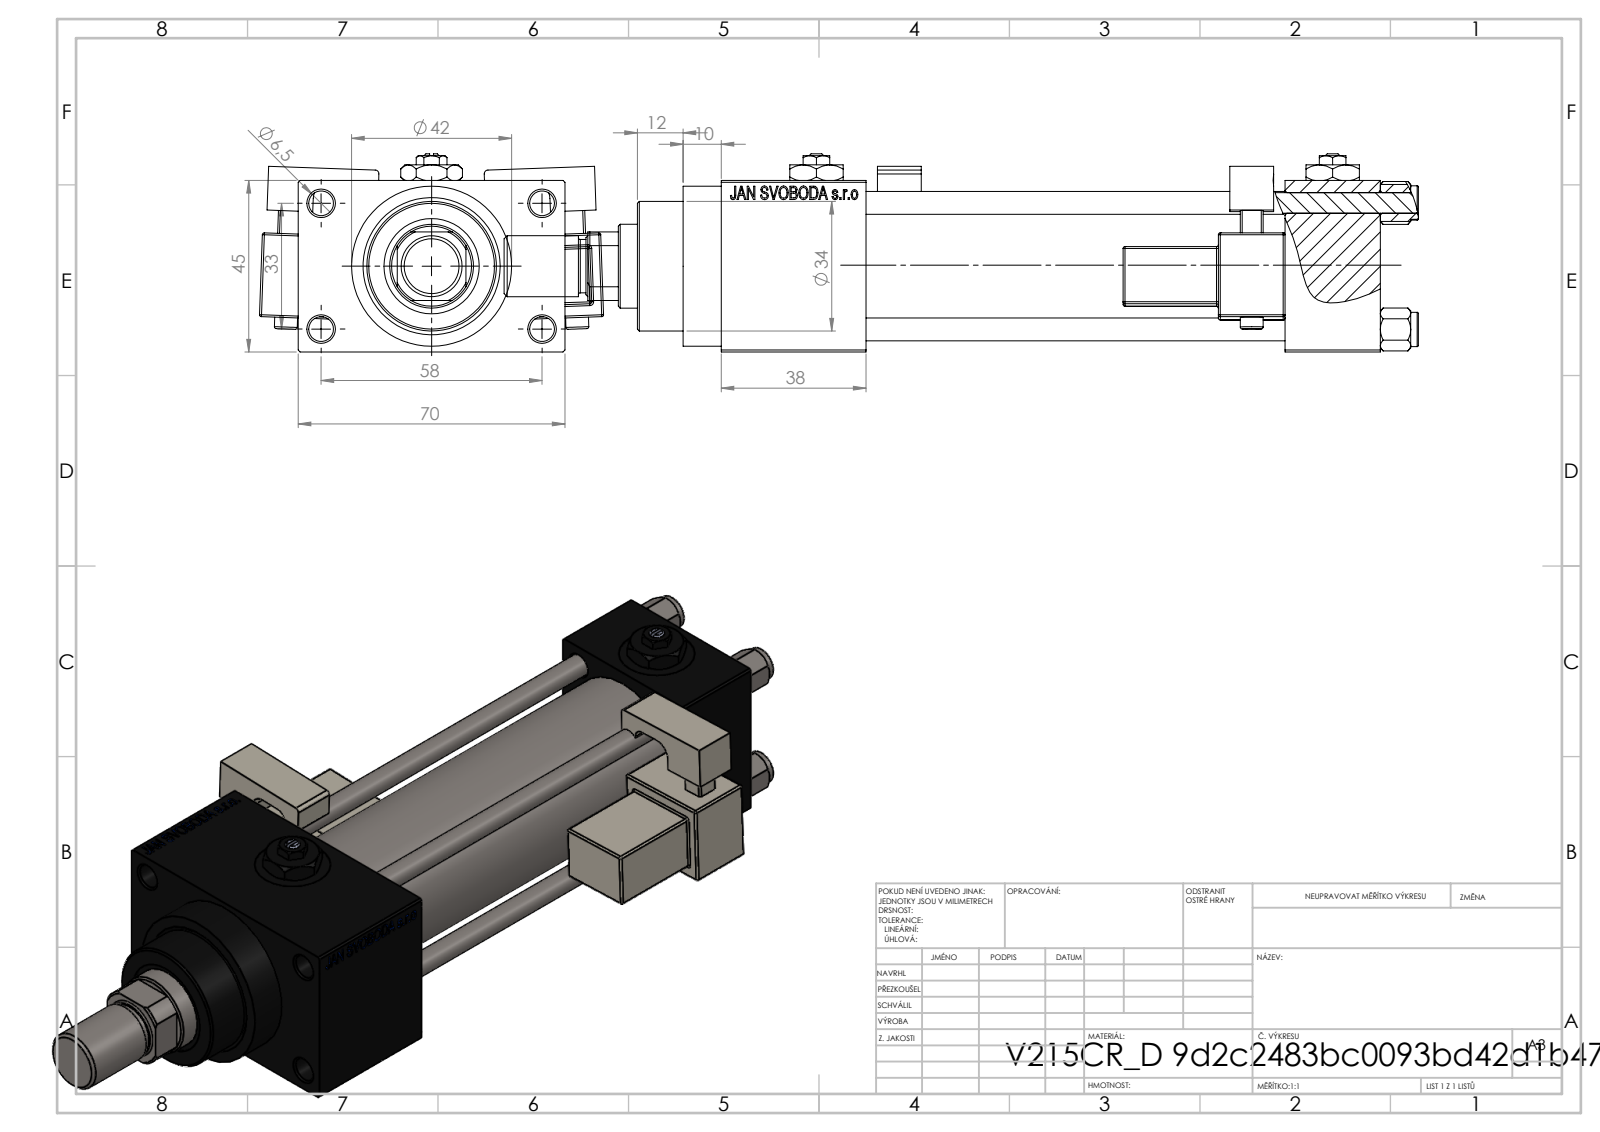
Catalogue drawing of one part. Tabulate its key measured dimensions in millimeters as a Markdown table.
| quantity | value |
| --- | --- |
| part name | V215CR_MSU; NUT_M5_D; V215CR_D_TYCINKA; ROD_END_AH (+4 more) |
| STEP written by | SolidWorks 2019 (CONFIG_CONTROL_DESIGN) |
| units | millimeters |
| bodies | 16 solids, 1375 faces (608 planar, 163 cylindrical, 604 other) |
| overall size | 240 × 90.31 × 52 |
| volume | 335 978 mm³ |
| surface area | 117 030 mm² |
| round holes (diameter × count) | 6 × 4, 6.5 × 4, 13.16 × 4, 20 × 4, 7 × 3, 10.5 × 1, 22 × 1, 24 × 1, 25 × 1, 32 × 1, 33 × 1 |
| round bosses / shafts (diameter × count) | 9 × 4, 6 × 2, 42 × 1, 38 × 1, 34 × 1, 16 × 1, 14 × 1 |
| partial cylindrical surfaces (radius × count) | 0.5 × 48, 1 × 2, 2.5 × 2, 4 × 2, 10.5 × 1 |
| main face-to-face distances | 45, 25, 110, 12.5, 3, 135, 57.5, 38, 148, 173 |
| hole center spacings | 12.4, 23.48, 33.2, 33.37, 35.35, 45.6, 56.35, 33 |
